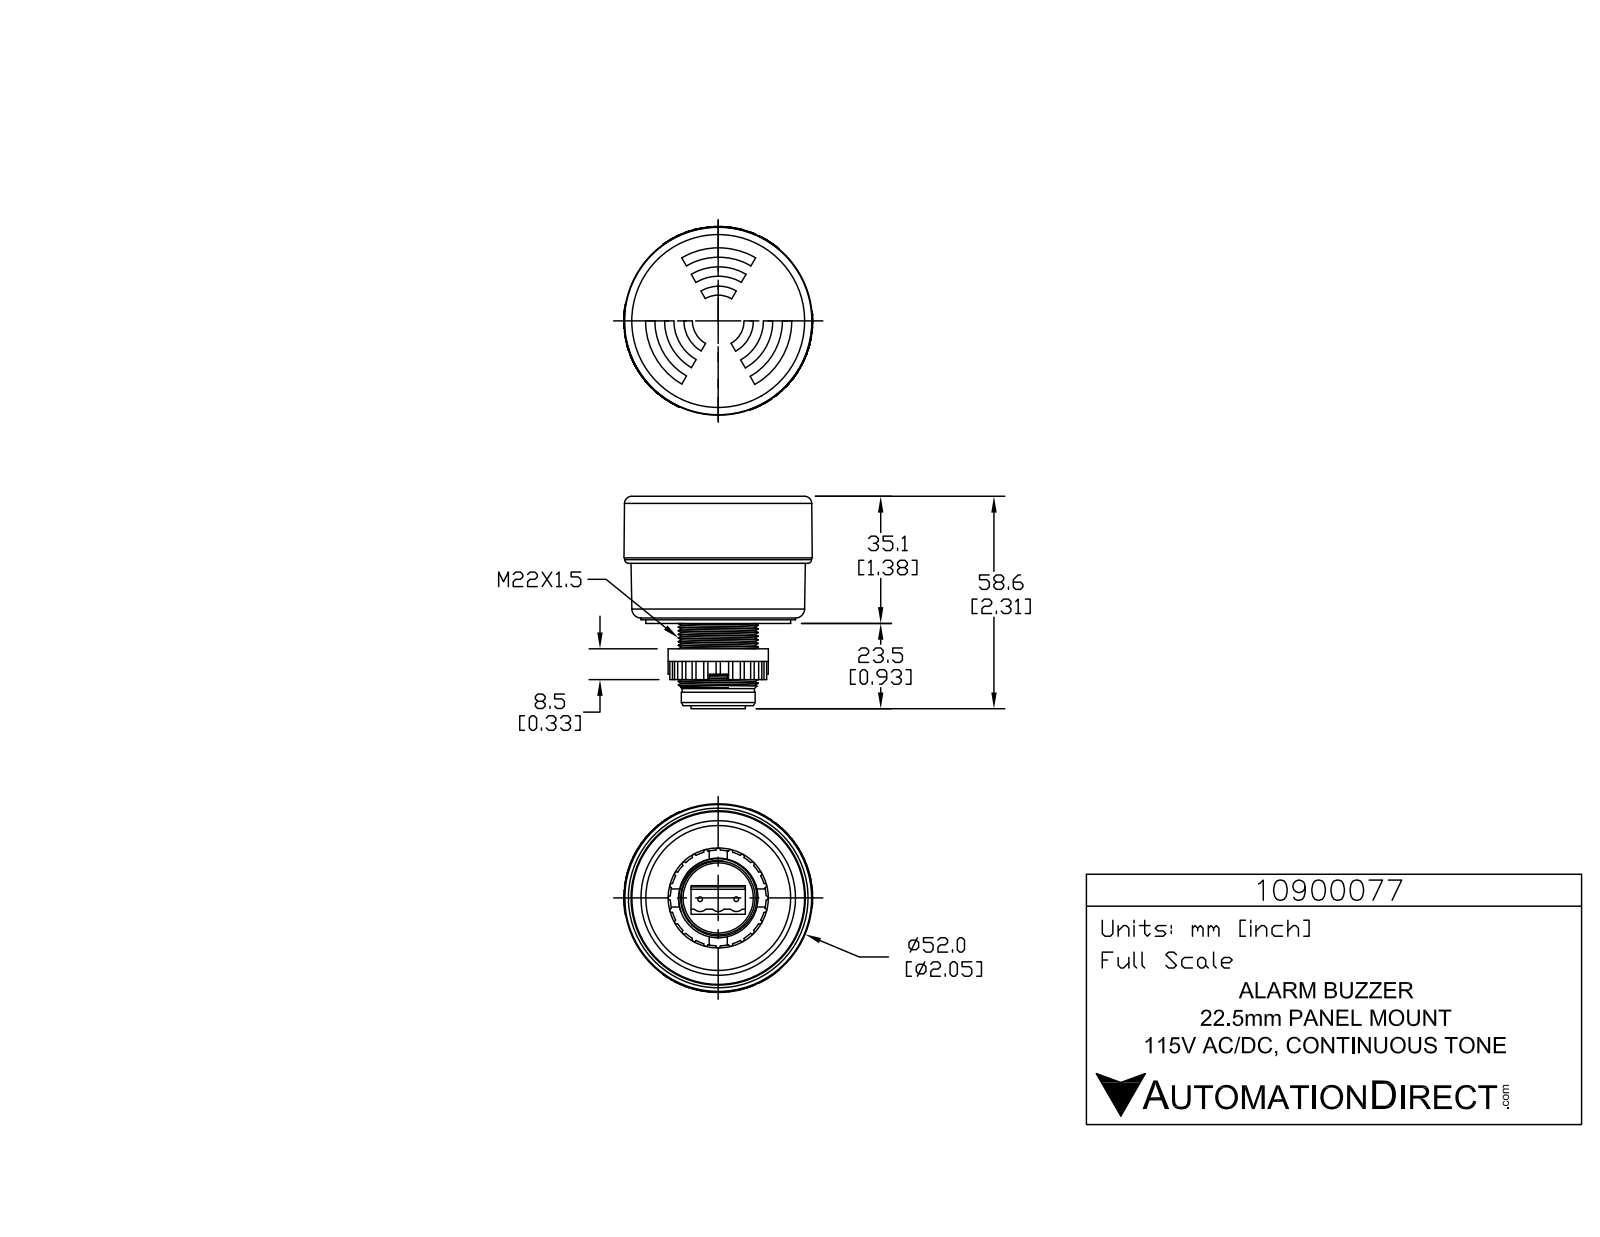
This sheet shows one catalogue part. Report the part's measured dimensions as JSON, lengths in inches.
{"part_name": "10900077", "step_written_by": "SolidWorks 2017 (AUTOMOTIVE_DESIGN)", "units": "inches", "bodies": {"solids": 1, "faces": 1180, "planar": 766, "cylindrical": 311, "other": 103}, "overall_size": [2.309, 2.054, 2.05], "volume_in3": 4.656, "surface_area_in2": 22.8, "round_holes": [[0.039, 4], [0.906, 1]], "round_bosses_or_shafts": [[0.226, 4], [0.056, 4], [0.051, 2], [2.031, 1], [1.681, 1], [1.575, 1], [1.091, 1], [0.866, 1]], "partial_cylinders_radius": [[0.023, 24], [0.008, 8], [0.008, 8], [0.008, 8], [0.131, 8], [0.004, 4], [0.005, 4], [0.008, 4]], "face_to_face_distances": [1.374, 0.276, 1.65, 0.039, 0.315, 1.335, 0.898, 0.937, 0.622, 2.272], "hole_center_spacings": [0.242]}
